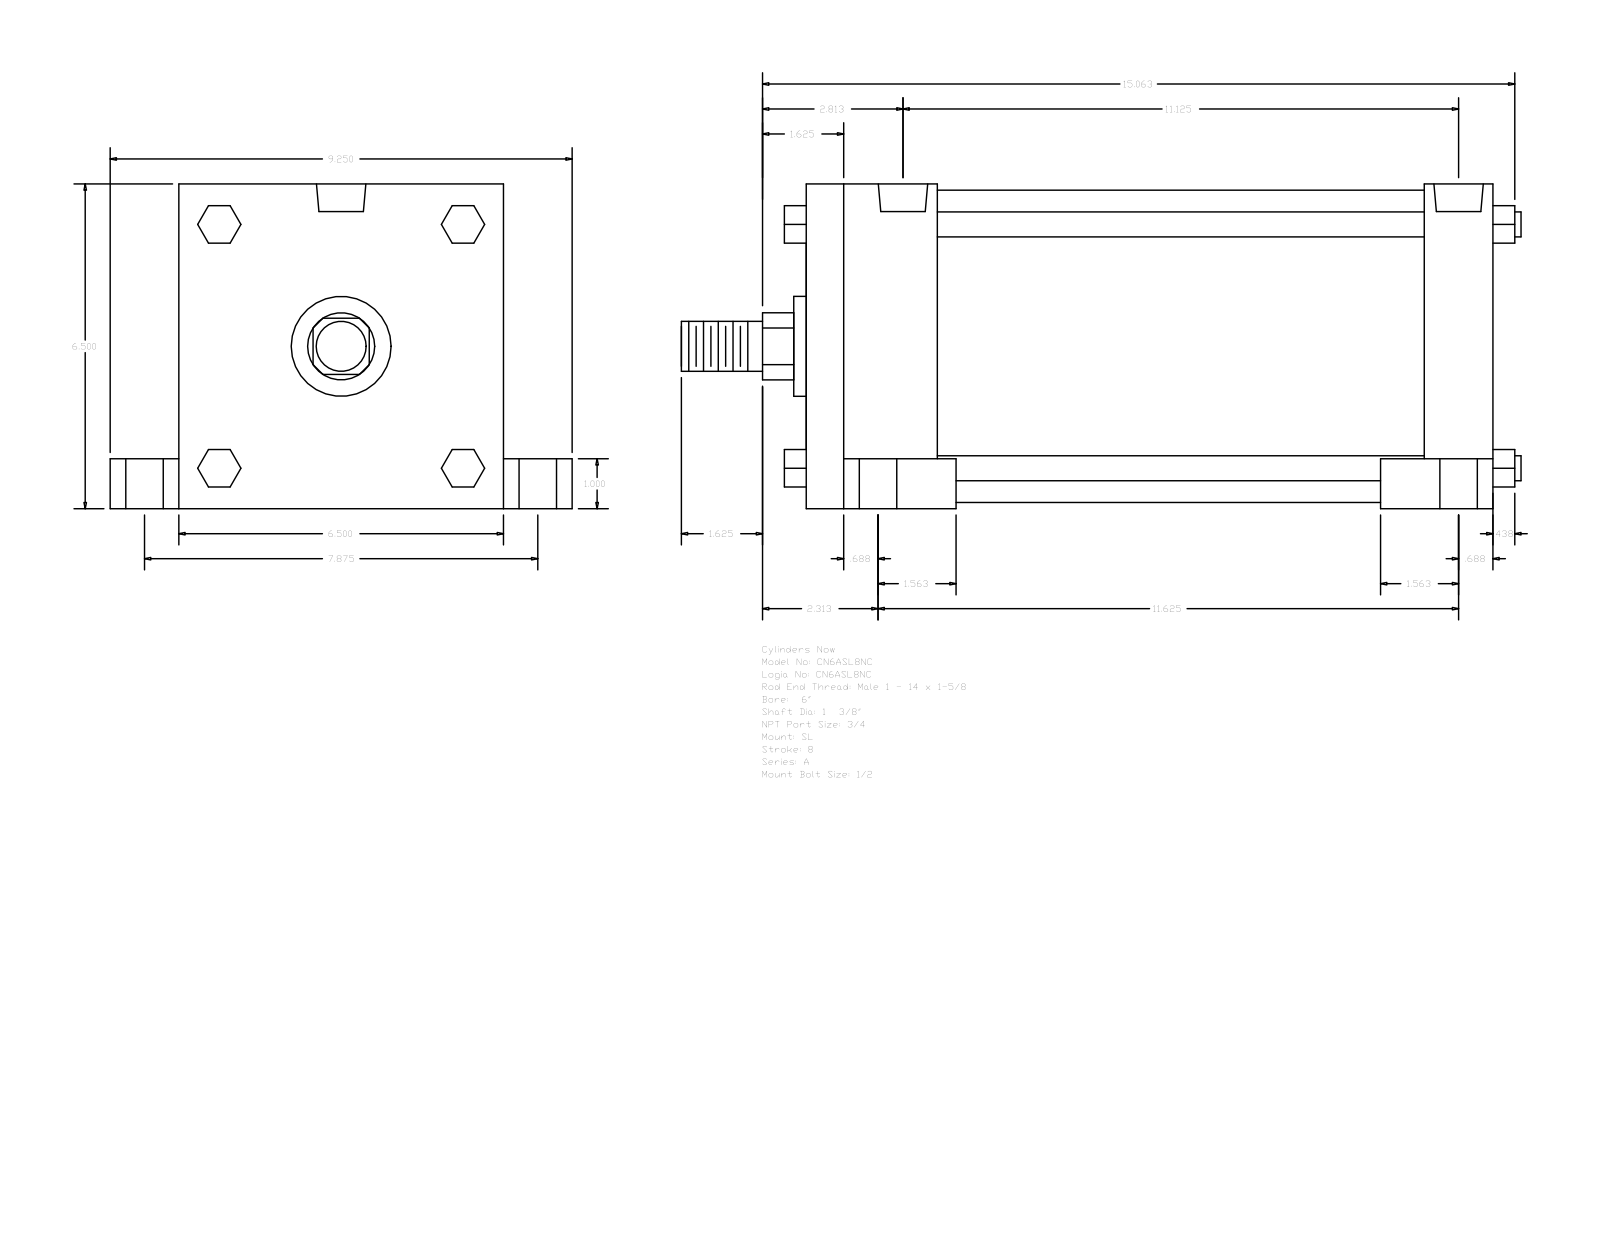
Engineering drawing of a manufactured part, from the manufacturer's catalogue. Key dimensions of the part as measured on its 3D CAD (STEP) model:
Part name (STEP PRODUCT): A_SL__0600_1.375
STEP written by: GSSL Pune (CONFIG_CONTROL_DESIGN)
Units: millimetres
Bodies: 0 solids, 150 faces (114 planar, 36 cylindrical, 0 other)
Overall size (bounding box): 427.04 × 234.95 × 165.1
Round holes (diameter × count): ⌀15.08 ×4, ⌀19.05 ×4, ⌀25.4 ×4, ⌀25.12 ×2
Round bosses / shafts (diameter × count): ⌀12.7 ×4, ⌀158.75 ×1, ⌀50.8 ×1, ⌀34.92 ×1, ⌀25.4 ×1
Partial cylindrical surfaces — rounded edges, fillets, slot ends (radius × count): R17.06 ×1
Main face-to-face distances: 165.1, 349.25, 314.32, 66.67, 282.58, 247.65, 34.93, 25.4, 139.7, 34.92
Hole centre spacings: 5.56, 100.01, 100.16, 100.81, 101.66, 200.02, 271.45, 277.01
